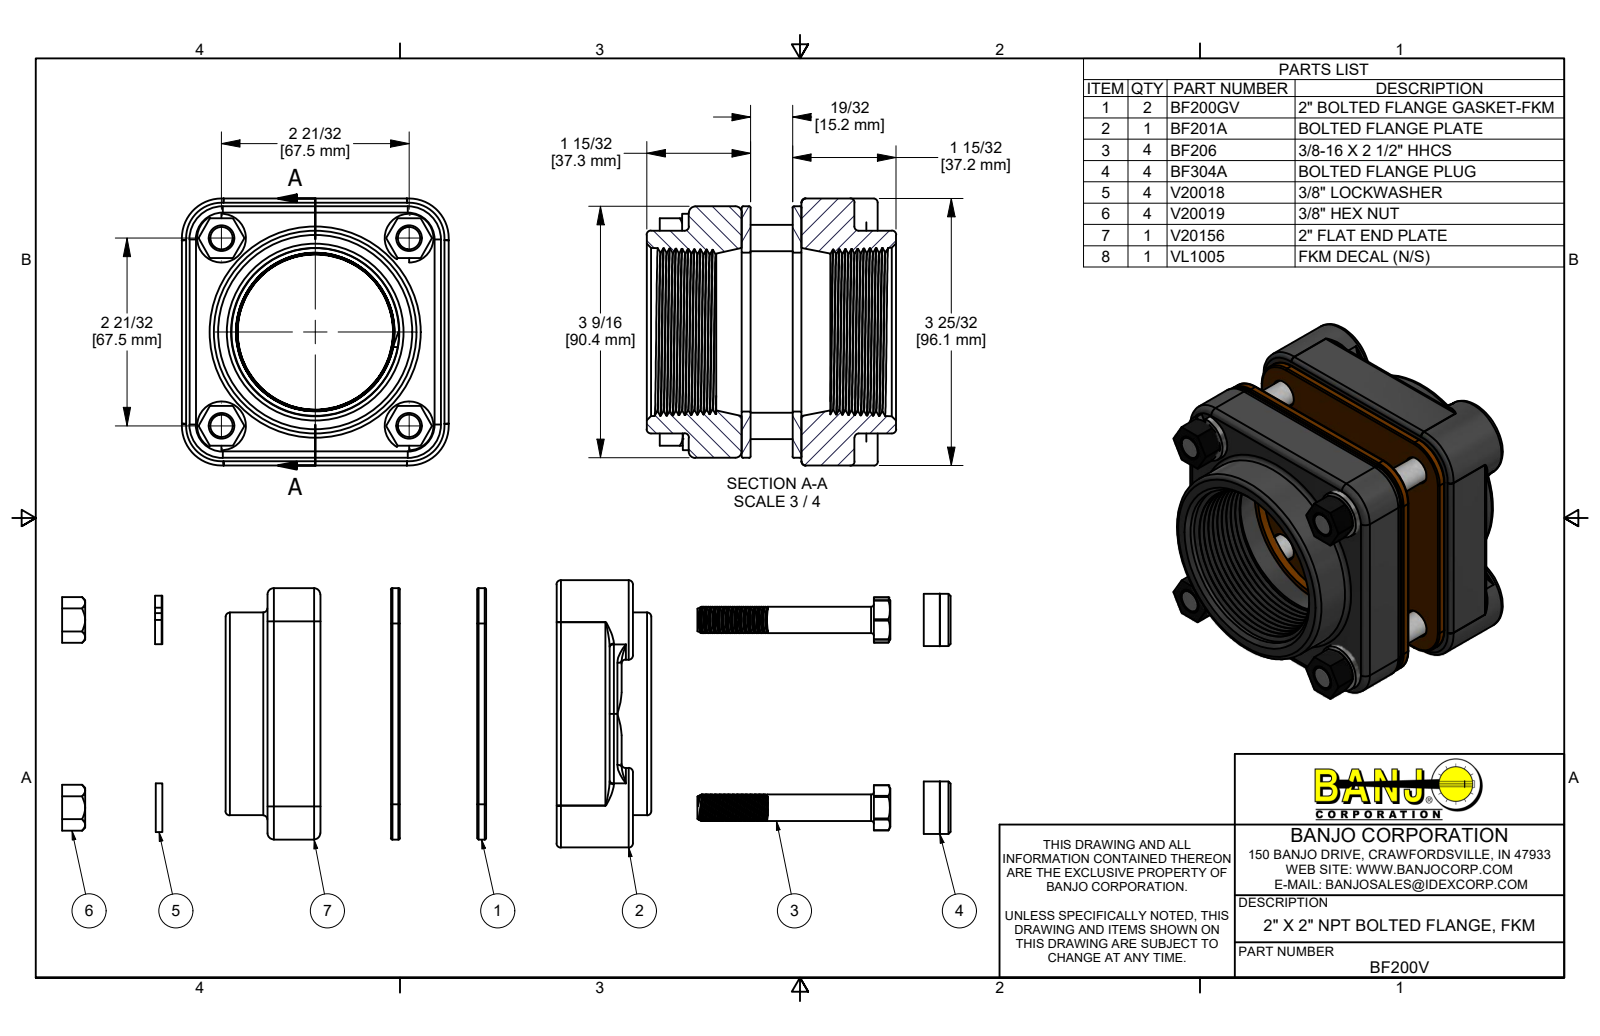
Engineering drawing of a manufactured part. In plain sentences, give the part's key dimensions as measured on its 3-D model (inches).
The part is named "BF200V; V20019; BF201A; V20156 (+4 more)". Its 3-D file was written by "Autodesk Inventor 2019 (AUTOMOTIVE_DESIGN)". It is 20 solids with 1122 faces: 315 planar, 344 cylindrical and 463 other. Overall it measures 38.352 by 3.784 by 3.784 inches. Its volume is 20.33 cubic inches and its surface area 452.6 square inches. Round holes: 4 of diameter 0.307, 4 of diameter 0.38, 4 of diameter 0.385, 4 of diameter 0.406, 4 of diameter 0.41, 4 of diameter 0.715, 4 of diameter 0.75, 1 of diameter 2.25. Round bosses or shafts: 60 of diameter 0.324, 4 of diameter 1.125, 4 of diameter 0.742, 4 of diameter 0.687, 4 of diameter 0.375, 1 of diameter 2.87. Partial cylindrical surfaces (rounded edges, fillets, slot ends): 16 of radius 0.02, 16 of radius 0.06, 8 of radius 0.09, 8 of radius 0.162, 4 of radius 0.32, 4 of radius 0.47, 4 of radius 0.5, 4 of radius 1.6. The main face-to-face distances are 0.847, 0.125, 0.722, 0.597, 0.722, 0.125, 0.111, 3.671, 0.75, 1.597. The hole center spacings are 1.88, 2.659, 3.761.
